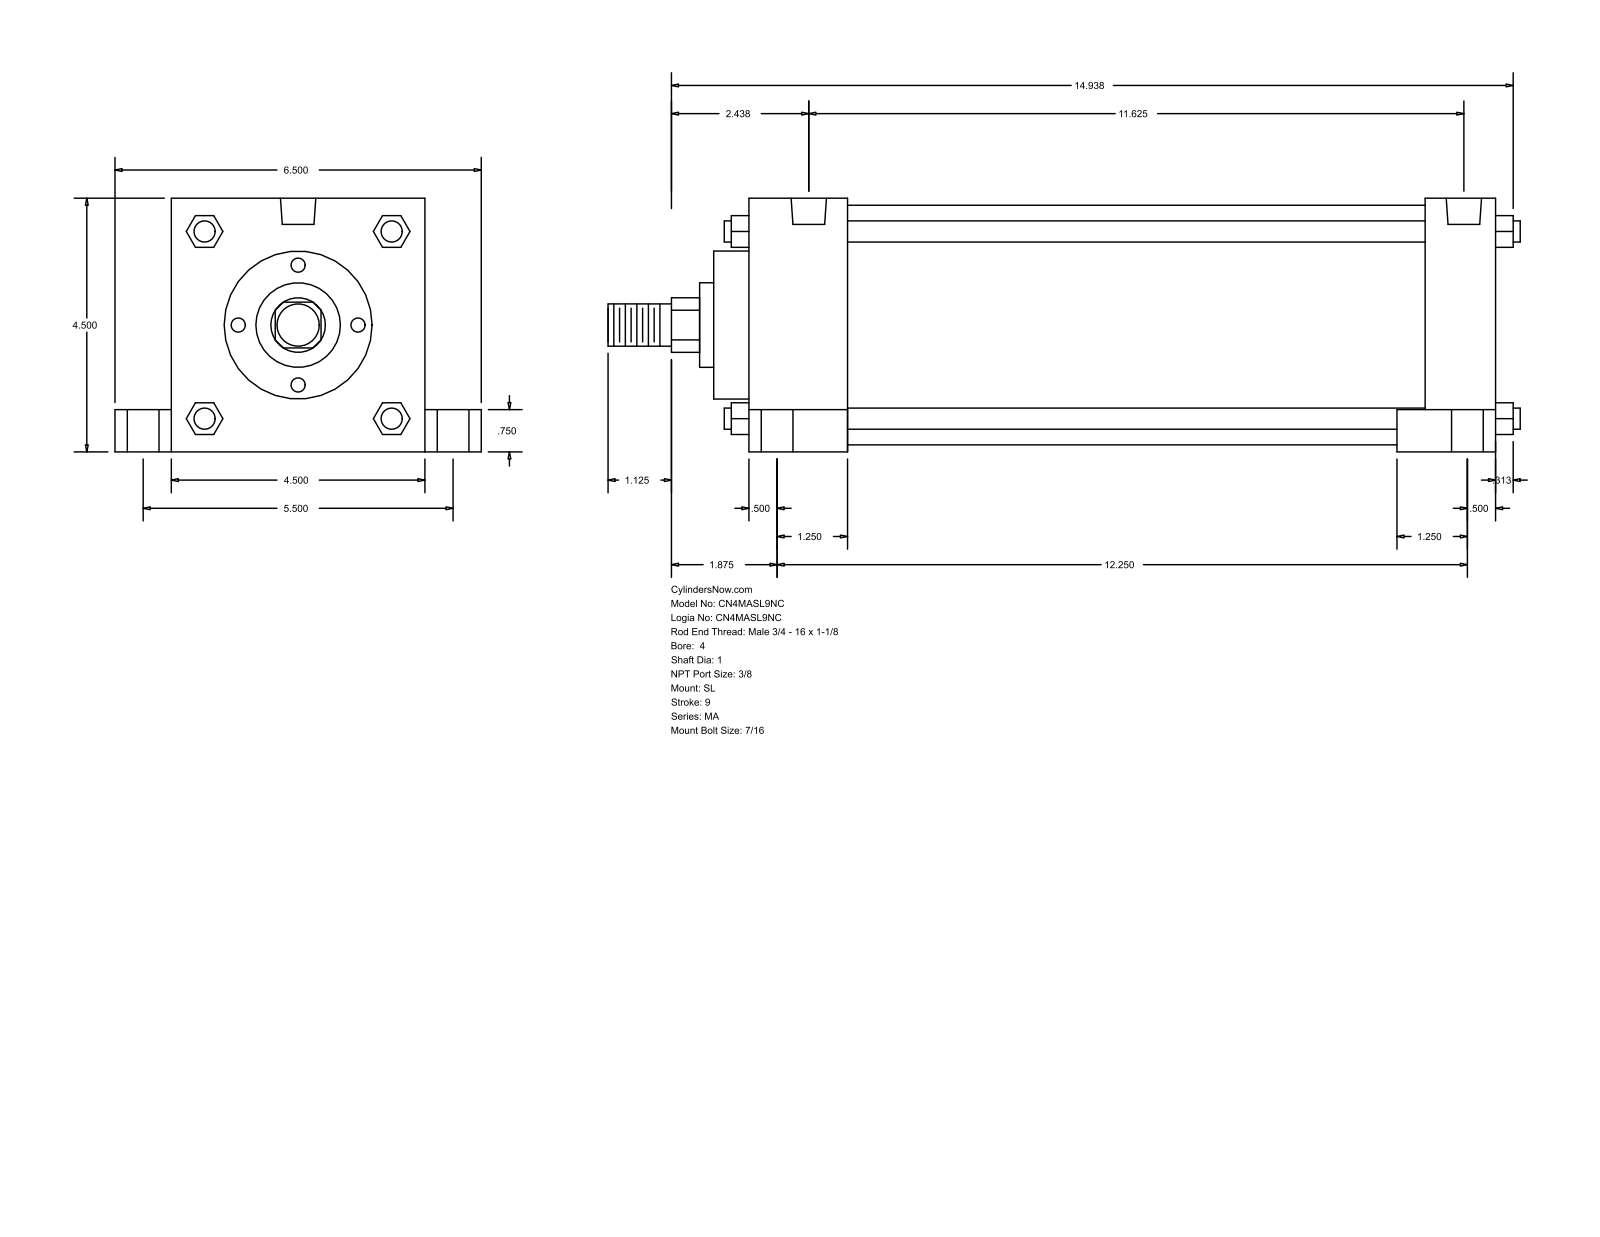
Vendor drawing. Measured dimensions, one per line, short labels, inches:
name: MA_SL__0400_1
written by: GSSL Pune (CONFIG_CONTROL_DESIGN)
unit: in
bodies: 0 solids, 150 faces (113 planar, 37 cylindrical, 0 other)
size: 16.187 × 6.5 × 4.5
holes: 4× ⌀0.437, 4× ⌀0.563, 4× ⌀0.813, 2× ⌀0.627
bosses: 4× ⌀0.375, 1× ⌀4.25, 1× ⌀2.625, 1× ⌀1.5, 1× ⌀1, 1× ⌀0.75
rounds: 1× R0.484
face distances: 4.5, 13.25, 10.25, 1.75, 11.5, 12, 1.25, 1, 5.5, 0.75
hole spacings: 0.187, 2.751, 2.761, 2.807, 2.85, 5.5, 11.25, 11.438
